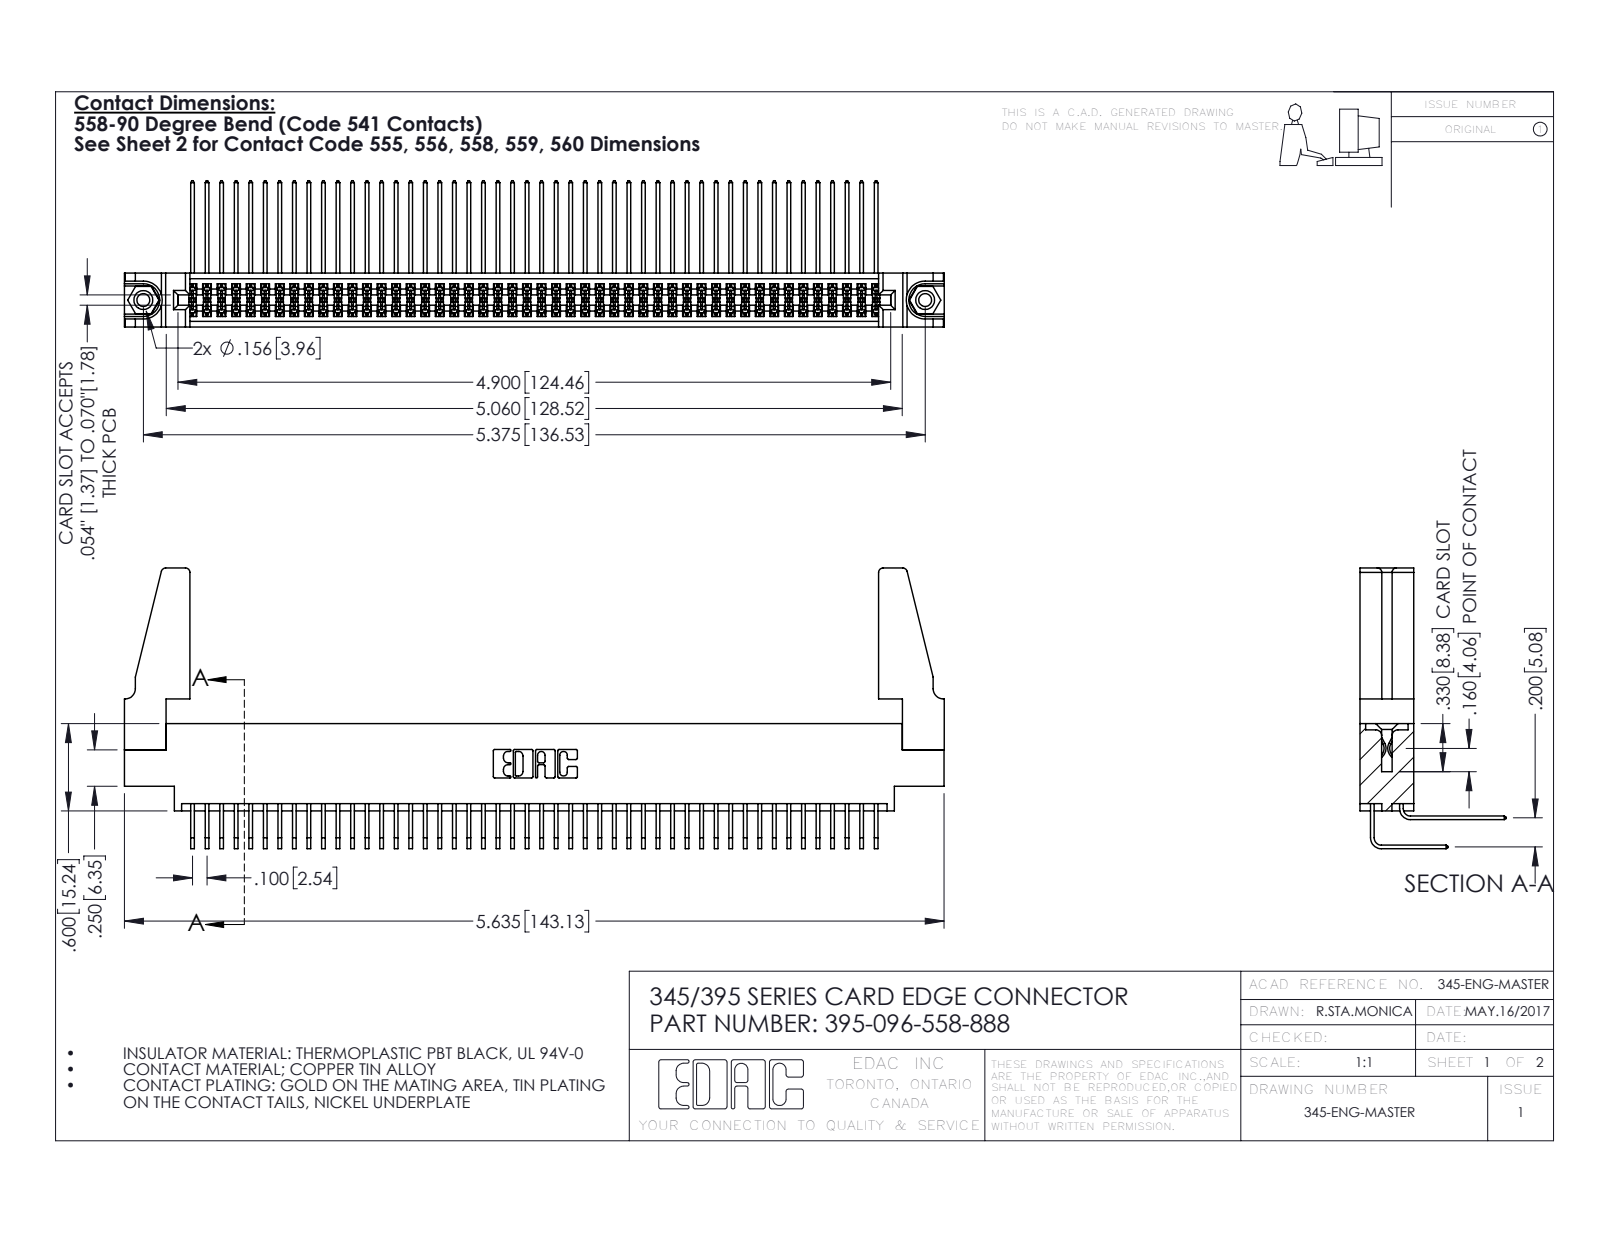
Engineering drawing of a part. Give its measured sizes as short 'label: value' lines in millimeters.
name: 345-292-001_558 Tail - 2; 345 Part_0.170 Offset - 0.156 Dia-TH; 395-096-558-888; 345-292-001_558 559 Tail - 1 (+2 more)
written by: SolidWorks 2016 (CONFIG_CONTROL_DESIGN)
unit: mm
bodies: 101 solids, 5246 faces (3516 planar, 1714 cylindrical, 16 other)
size: 143.2 × 49 × 25.5
volume: 17 650 mm³; area: 27 280 mm²
holes: 2× ⌀2.3, 2× ⌀3.2, 2× ⌀4, 1× ⌀1.6
bosses: 2× ⌀3.9
rounds: 145× R0.2, 22× R0.3, 8× R0.8, 6× R0.2, 6× R0.8, 3× R0.7, 2× R0.4, 2× R0.5
face distances: 1.8, 7.6, 9.4, 5.1, 2.5, 6.9, 0.6, 5.7, 4.4, 0.6
hole spacings: 6.9, 130.5, 136.5
